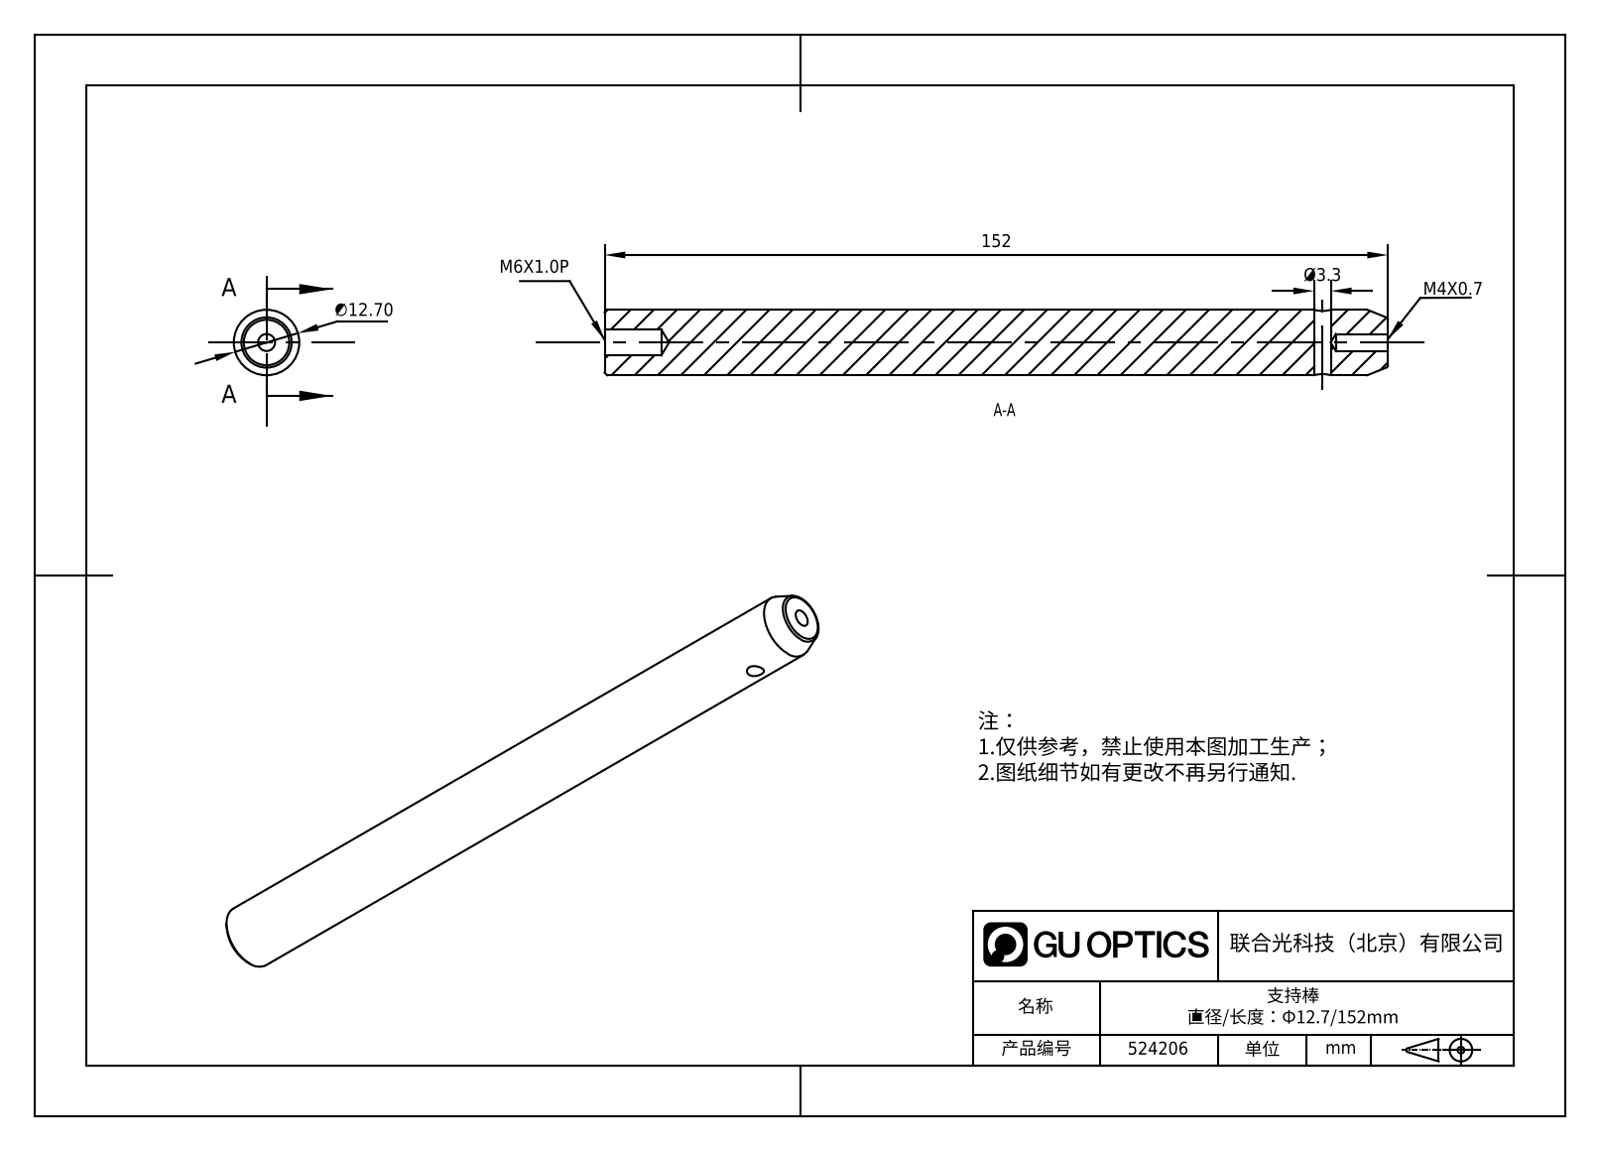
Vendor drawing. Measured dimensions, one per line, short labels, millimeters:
name: 524206
written by: SolidWorks 2016 (AUTOMOTIVE_DESIGN)
unit: mm
bodies: 1 solid, 20 faces (2 planar, 8 cylindrical, 10 other)
size: 152 × 12.7 × 12.7
volume: 18 710 mm³; area: 6 633 mm²
holes: 2× ⌀3.3, 1× ⌀5
bosses: 1× ⌀12.7
face distances: 152
